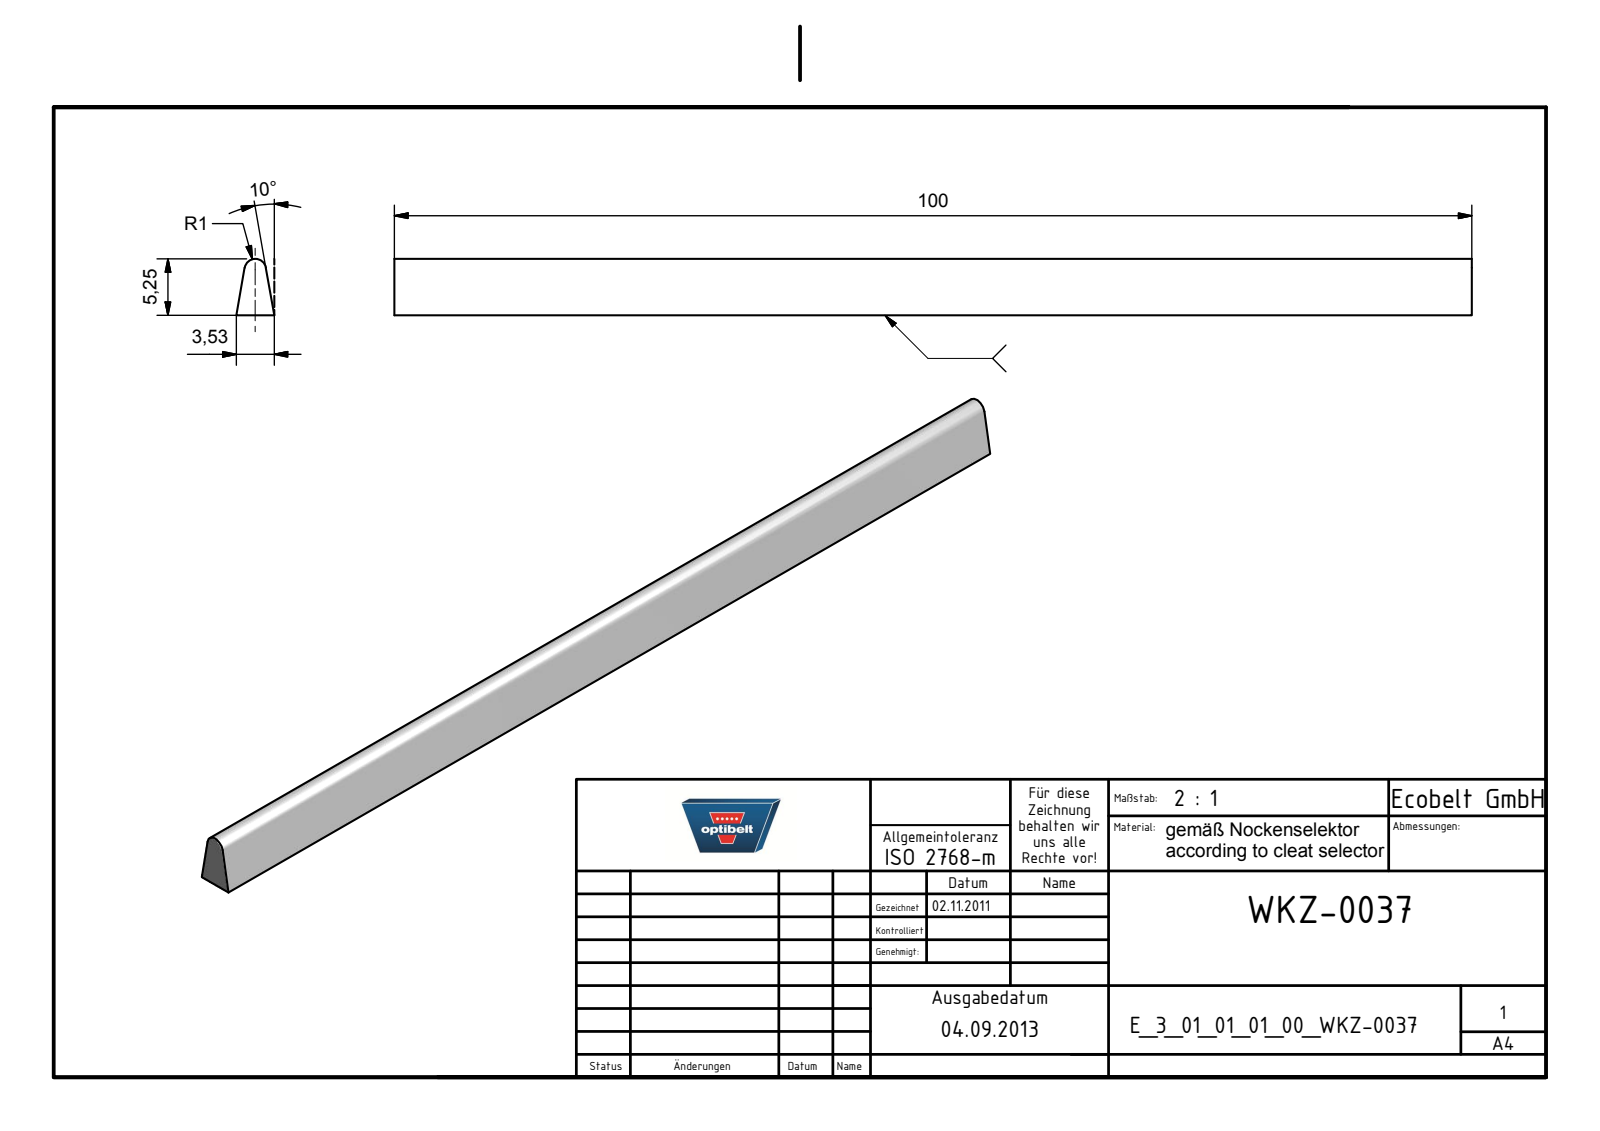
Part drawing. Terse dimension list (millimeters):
name: E_3_01_01_01_00_WKZ-0037
written by: Autodesk Inventor 2021 (AUTOMOTIVE_DESIGN)
unit: mm
bodies: 1 solid, 6 faces (5 planar, 1 cylindrical, 0 other)
size: 100 × 5.25 × 3.53
volume: 1 339 mm³; area: 1 557 mm²
rounds: 1× R1
face distances: 100
